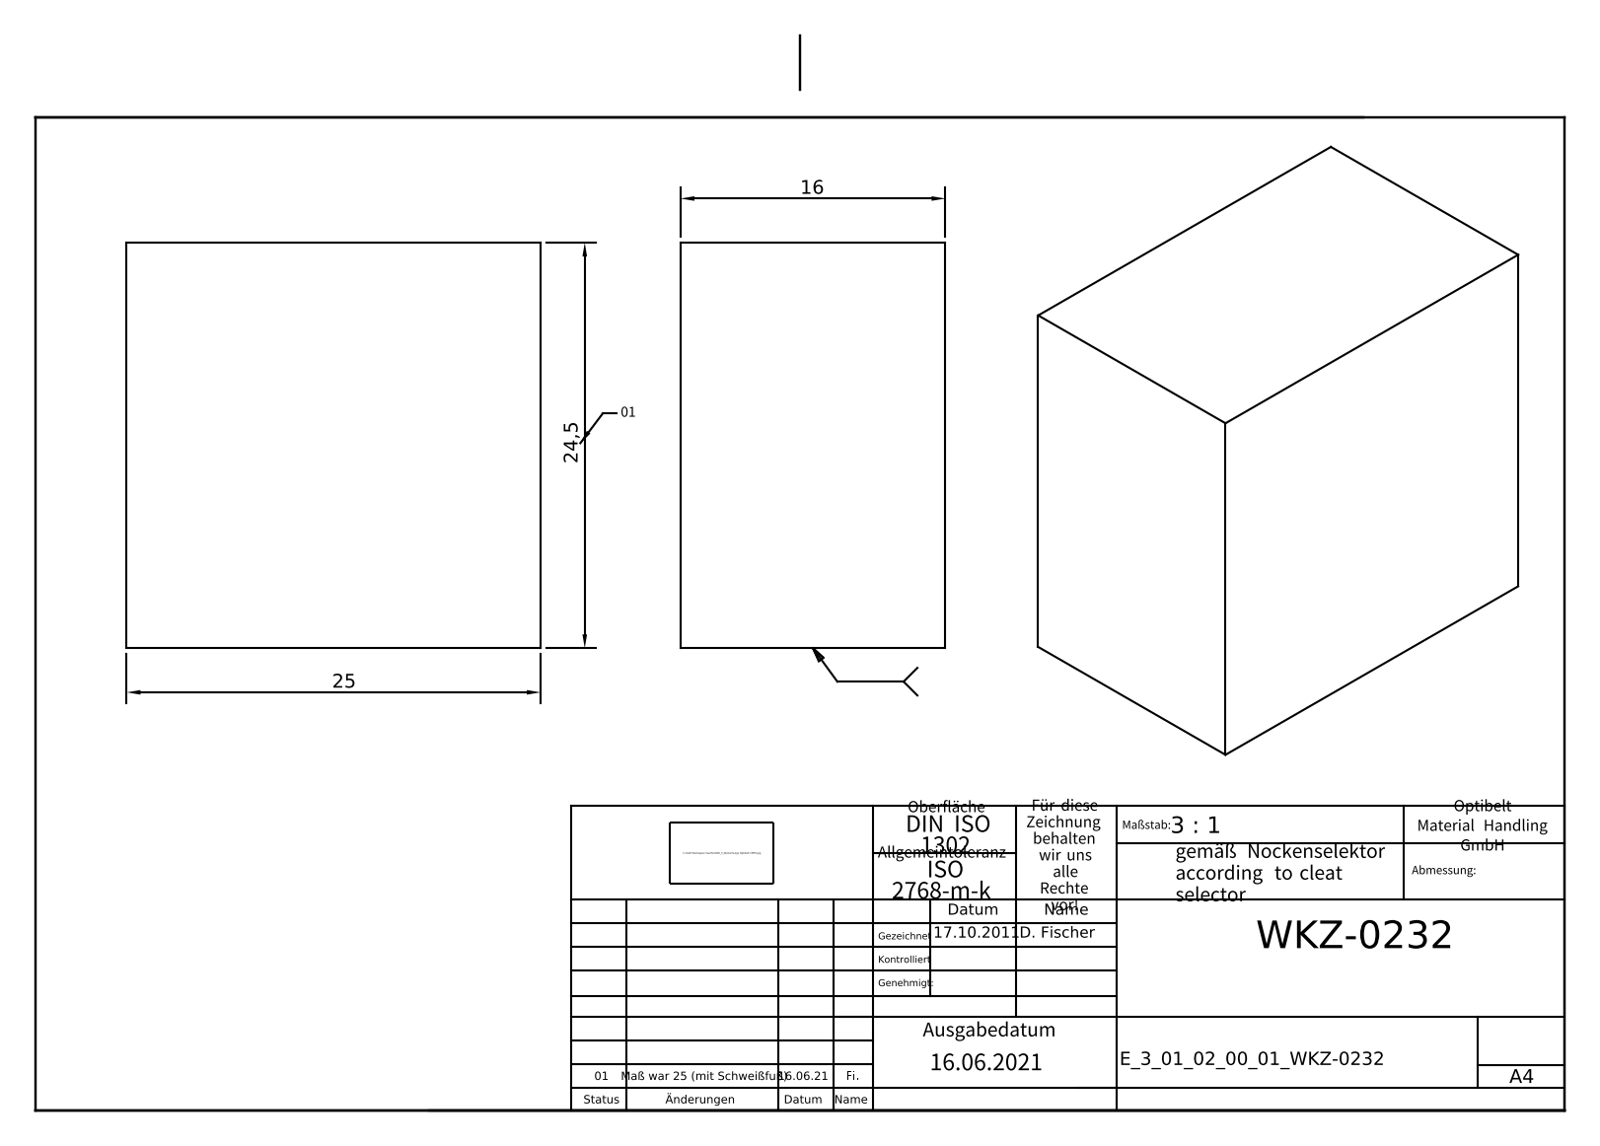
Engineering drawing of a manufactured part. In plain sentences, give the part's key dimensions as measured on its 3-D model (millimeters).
The part is named "E_3_01_02_00_01_WKZ-0232". Its 3-D file was written by "Autodesk Inventor 2021 (AUTOMOTIVE_DESIGN)". It is 1 solid with 6 faces: 6 planar, 0 cylindrical and 0 other. Overall it measures 25 by 24.5 by 16 millimeters. Its volume is 9 800 cubic millimeters and its surface area 2 809 square millimeters. The main face-to-face distances are 16, 24.5, 25.
